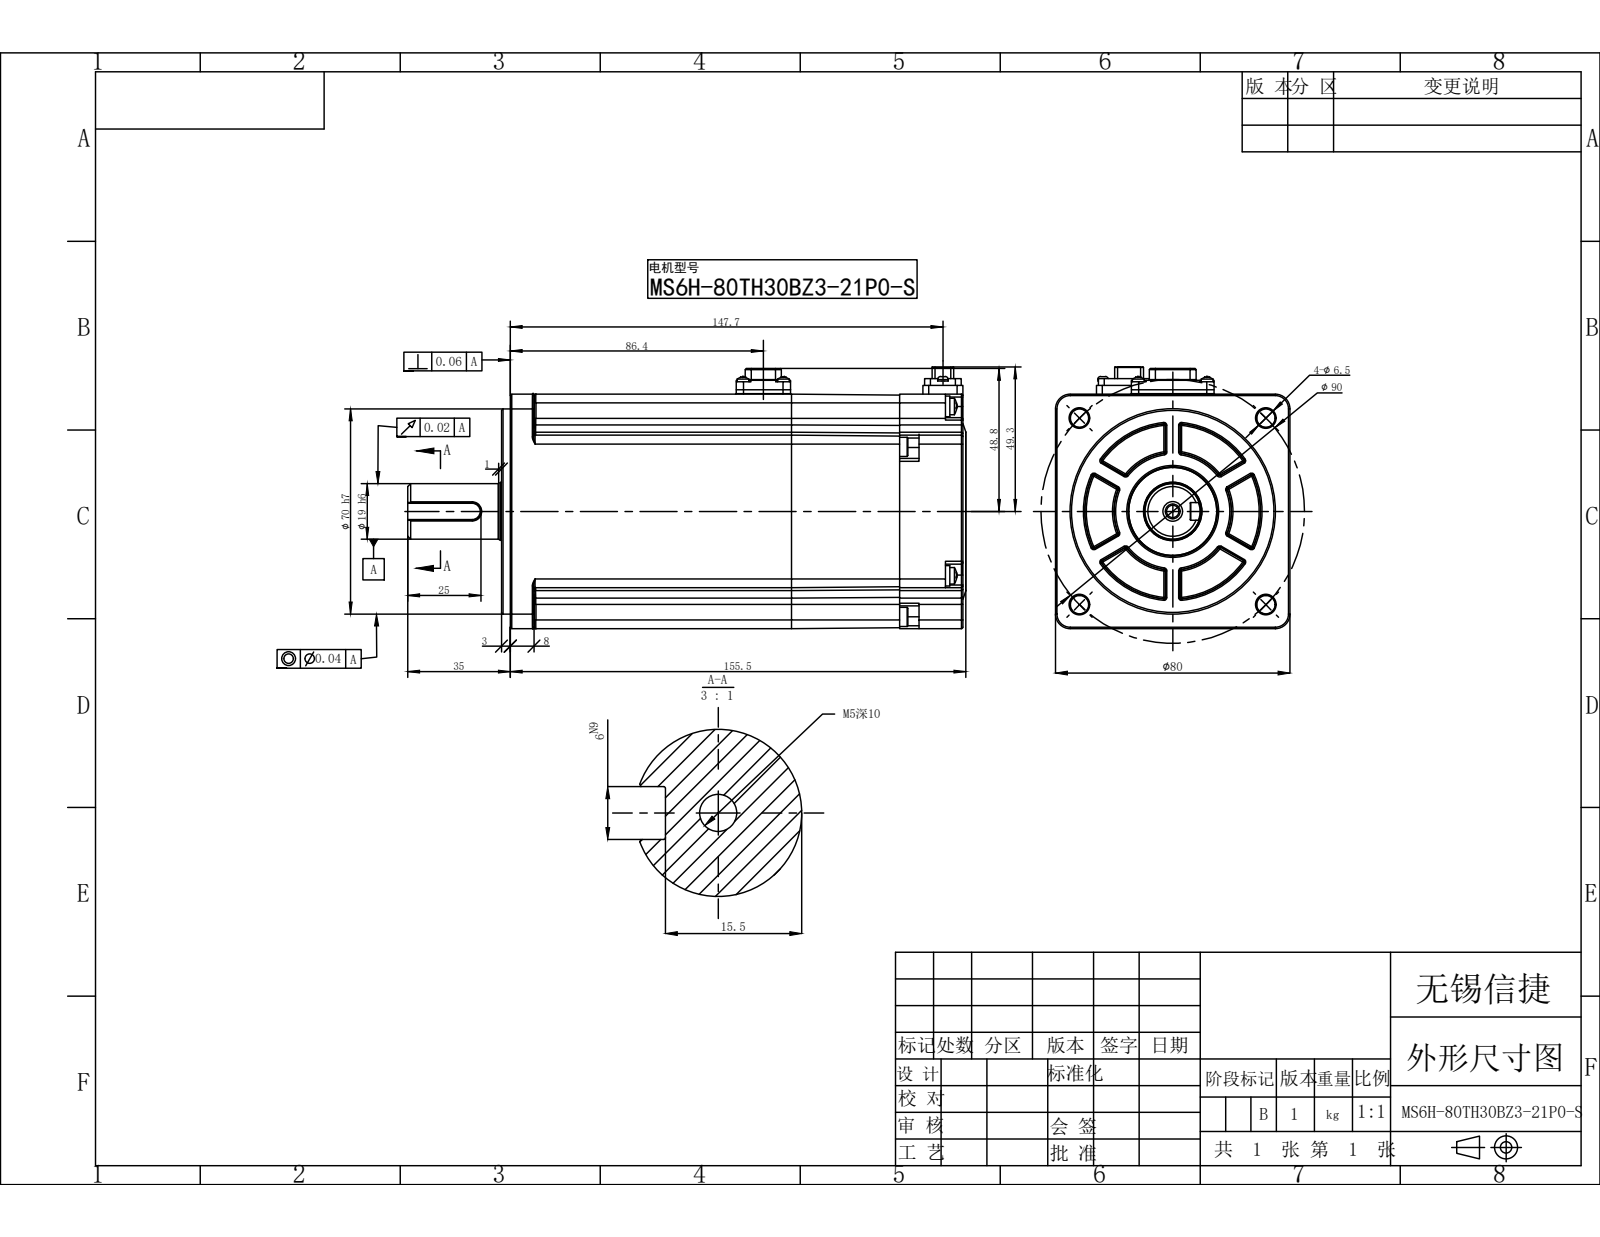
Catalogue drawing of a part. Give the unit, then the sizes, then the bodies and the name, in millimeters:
Units: millimetres
Overall size (bounding box): 190.5 × 89.3 × 80
Round holes (diameter × count): ⌀2.1 ×4, ⌀1.6 ×2, ⌀4.2 ×1, ⌀20 ×1
Round bosses / shafts (diameter × count): ⌀7 ×4, ⌀6.53 ×4, ⌀5.6 ×4, ⌀4 ×4, ⌀3.5 ×2, ⌀70 ×1, ⌀30 ×1, ⌀19.8 ×1
Partial cylindrical surfaces — rounded edges, fillets, slot ends (radius × count): R0.5 ×50, R0.2 ×20, R1 ×20, R3 ×17, R0.59 ×13, R2 ×12, R0.3 ×10, R3.75 ×8
Main face-to-face distances: 80, 14, 66, 1, 155.5, 154.5, 52, 3, 21.6, 22.6
Hole centre spacings: 8, 16.6, 18.43, 23.5, 57.53, 58.43, 60.17, 65.5
Bodies: 0 solids, 948 faces (353 planar, 280 cylindrical, 315 other)
Part name (STEP PRODUCT): MS6H-80TH30BZ3-21P0-S
STEP written by: SolidWorks 2022 (CONFIG_CONTROL_DESIGN)
